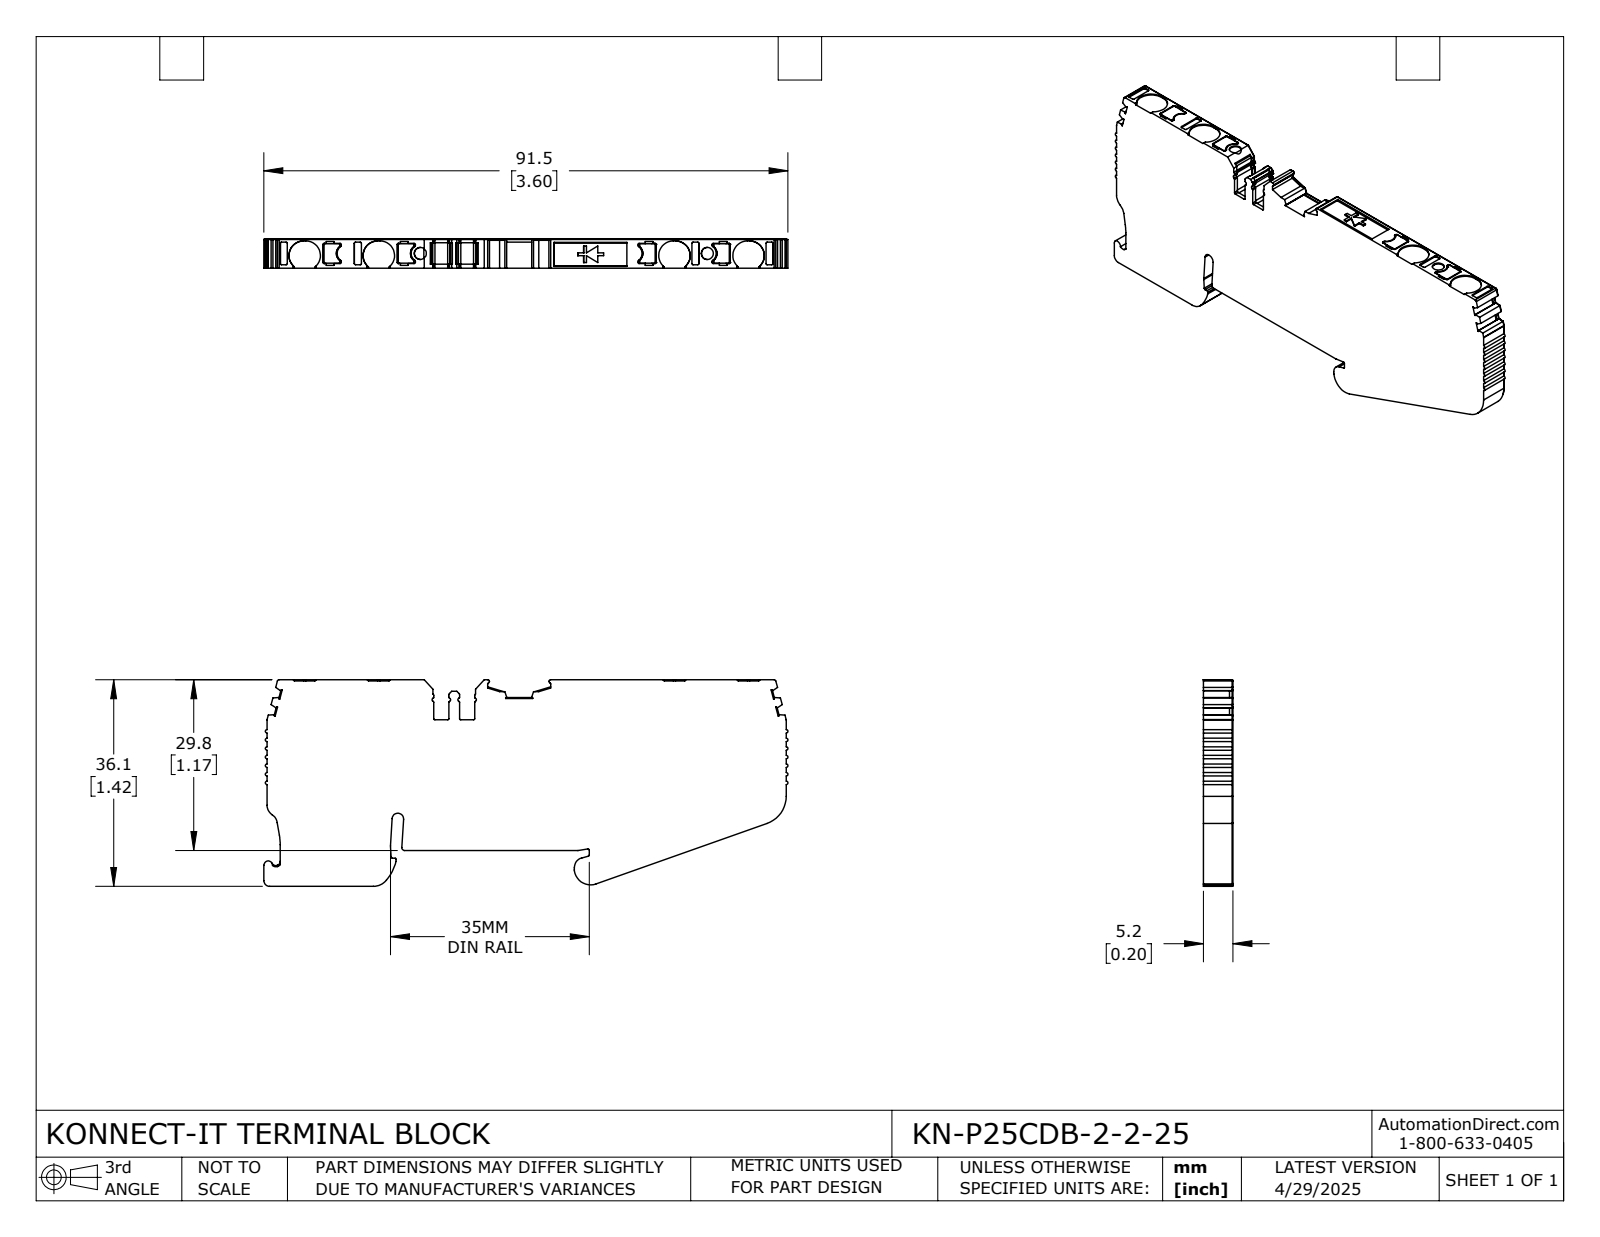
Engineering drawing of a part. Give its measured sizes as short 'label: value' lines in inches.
name: KN-P25CDB-2-2-25
written by: SolidWorks 2024 (CONFIG_CONTROL_DESIGN)
unit: in
bodies: 1 solid, 647 faces (371 planar, 273 cylindrical, 3 other)
size: 3.602 × 1.42 × 0.203
volume: 0.855 in³; area: 11.08 in²
holes: 2× ⌀0.083
rounds: 78× R0.008, 39× R0.012, 16× R0.006, 16× R0.02, 13× R0.004, 9× R0.016, 8× R0.1, 4× R0.059
face distances: 0.203, 1.166, 1.174, 0.246, 1.412, 1.42, 3.569, 0.197, 0.177, 0.047
hole spacings: 1.973
